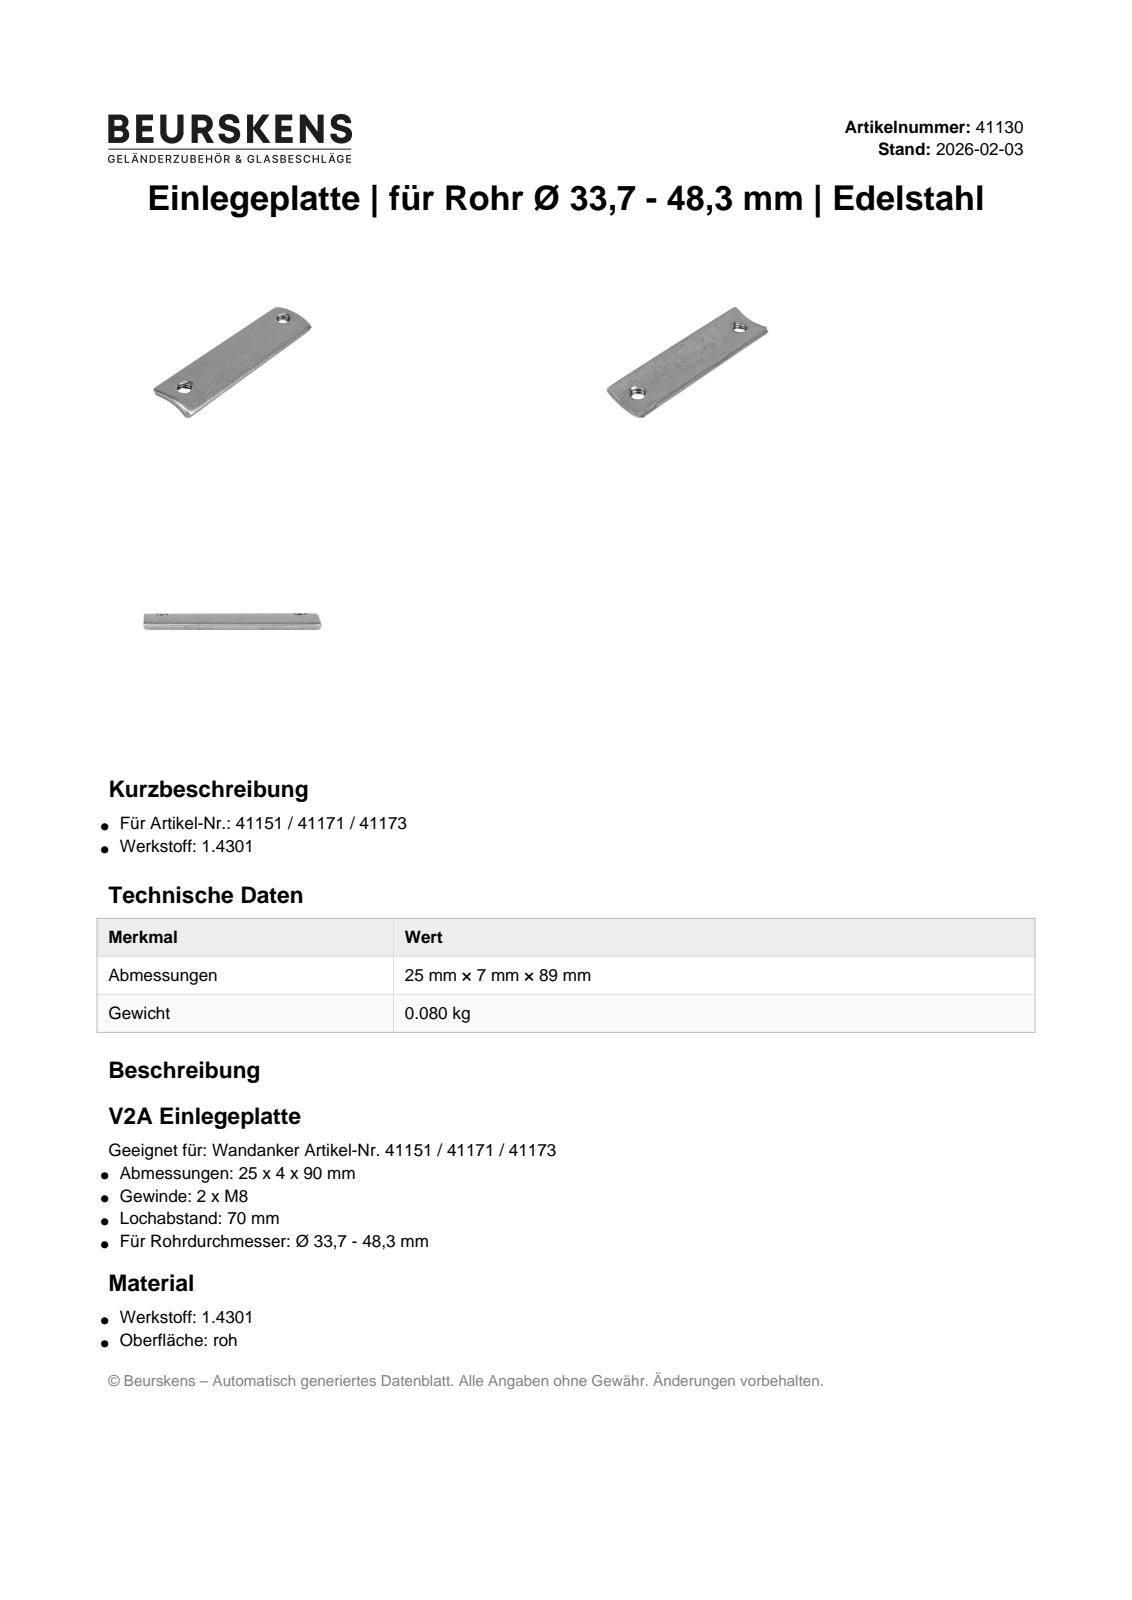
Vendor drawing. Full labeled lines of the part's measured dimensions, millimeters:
Part name (STEP PRODUCT): 41130
STEP written by: Autodesk Inventor 2022 (AUTOMOTIVE_DESIGN)
Units: millimetres
Bodies: 1 solid, 8 faces (4 planar, 4 cylindrical, 0 other)
Overall size (bounding box): 90 × 25 × 8.08
Volume: 8 598 mm³ · Surface area: 5 732 mm²
Round holes (diameter × count): ⌀8 ×2
Partial cylindrical surfaces — rounded edges, fillets, slot ends (radius × count): R21.2 ×2
Main face-to-face distances: 25, 90
Hole centre spacings: 70
